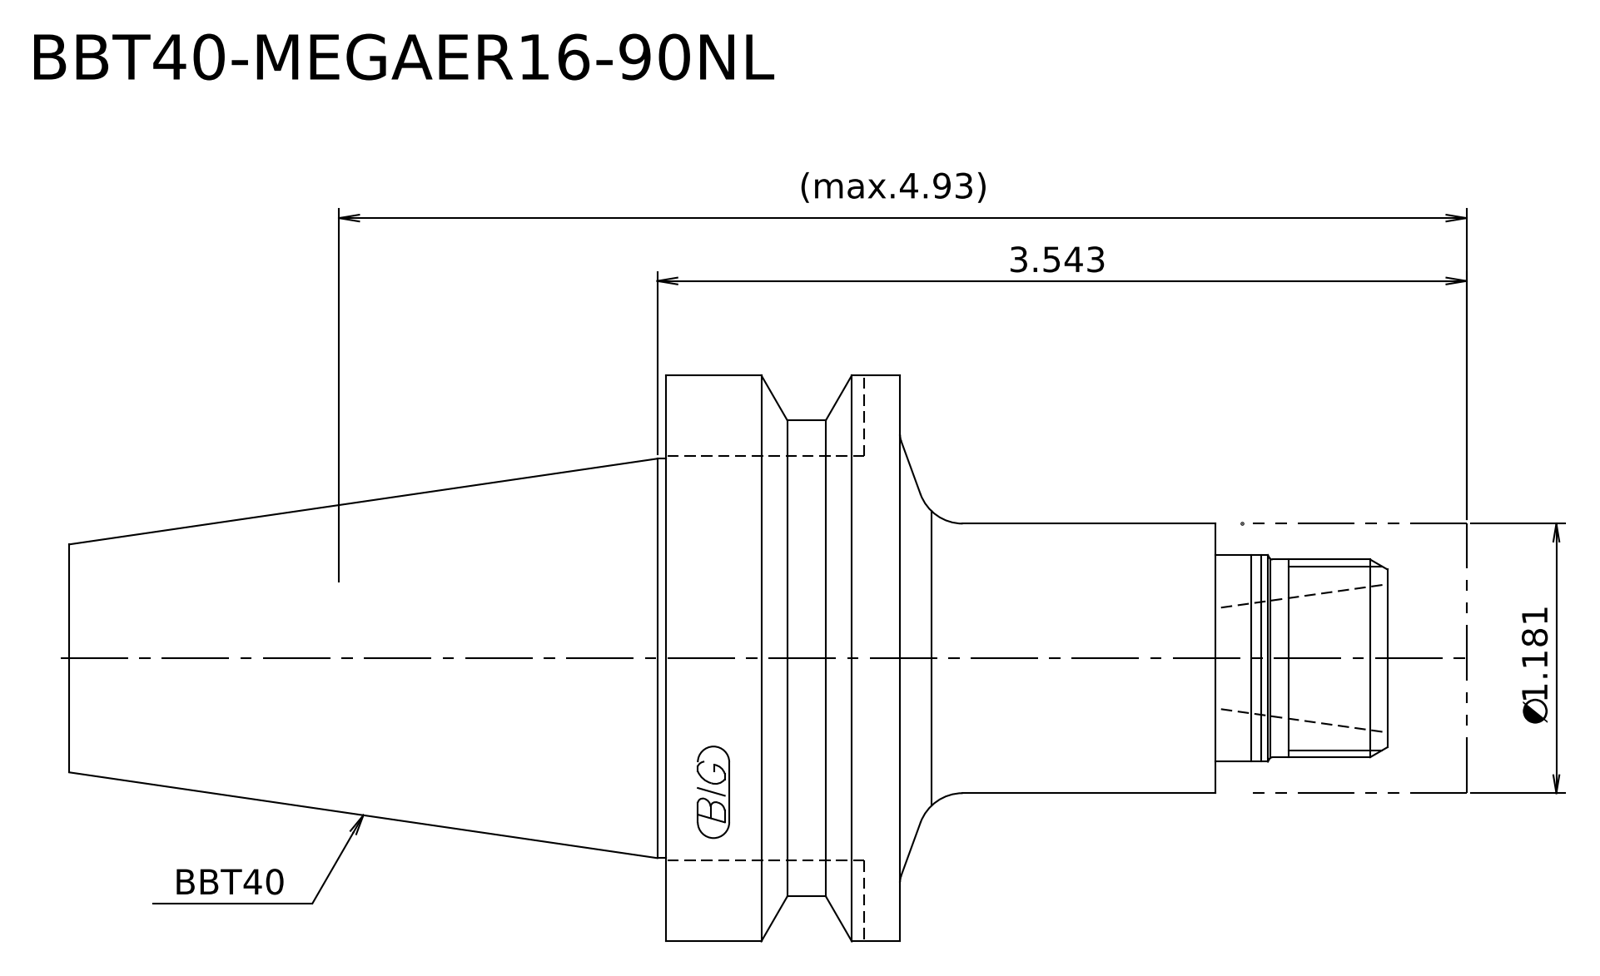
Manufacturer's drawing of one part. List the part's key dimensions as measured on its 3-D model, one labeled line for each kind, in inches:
STEP written by: Kubotek KeyCreator 2011 V10.0.2 (22737) (automotive_design)
Units: inches
Bodies: 2 solids, 21 faces (7 planar, 8 cylindrical, 6 other)
Overall size (bounding box): 6.118 × 2.48 × 2.48
Volume: 11.84 in³ · Surface area: 41.09 in²
Round bosses / shafts (diameter × count): ⌀2.48 ×1, ⌀2.087 ×1, ⌀1.75 ×1, ⌀1.181 ×1, ⌀0.906 ×1, ⌀0.866 ×1
Main face-to-face distances: 1.024, 1.496, 2.52, 0.984, 2.48, 3.504, 6.118, 5.134, 3.638, 2.614
